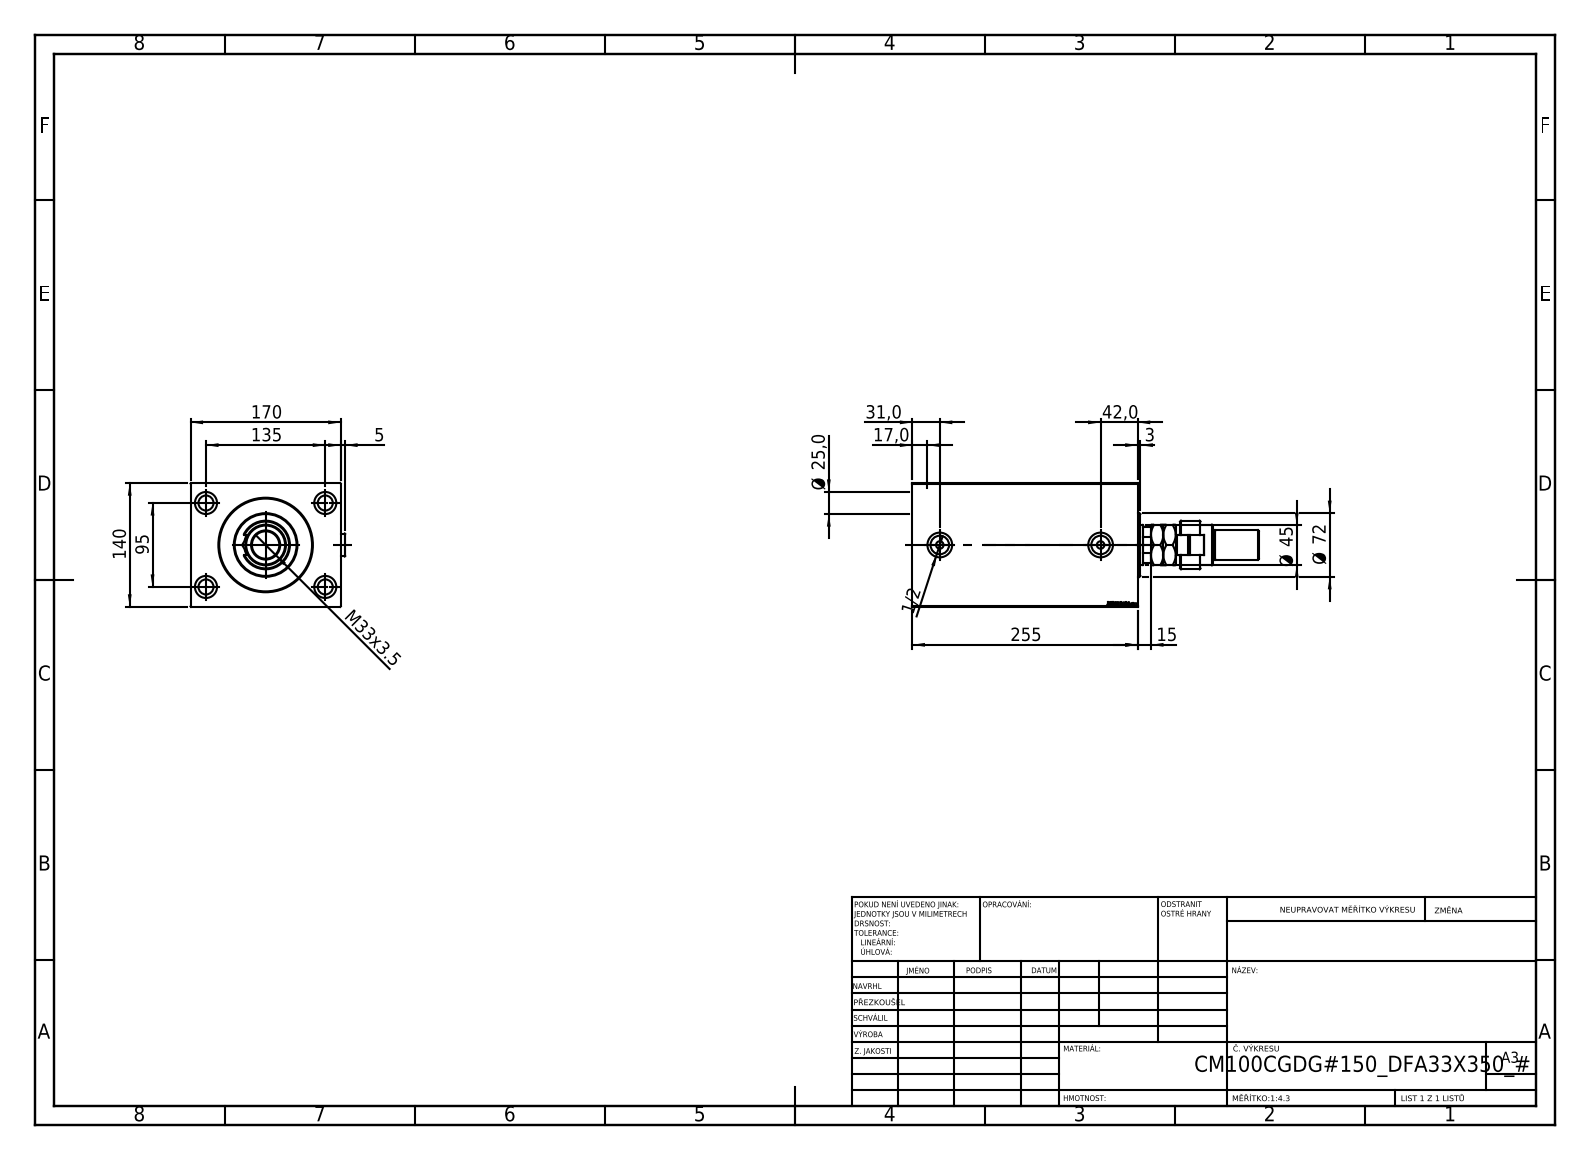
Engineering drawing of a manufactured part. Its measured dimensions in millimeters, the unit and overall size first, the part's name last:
Units: millimetres
Overall size (bounding box): 392 × 174.9 × 140
Round holes (diameter × count): ⌀17 ×4, ⌀25 ×4, ⌀8.5 ×2, ⌀20.96 ×2, ⌀28 ×2, ⌀31.5 ×1, ⌀39 ×1, ⌀45 ×1, ⌀48.5 ×1, ⌀100 ×1, ⌀102 ×1, ⌀105 ×1
Round bosses / shafts (diameter × count): ⌀26 ×2, ⌀72 ×1, ⌀55 ×1, ⌀46 ×1, ⌀35 ×1, ⌀33 ×1, ⌀31 ×1, ⌀22 ×1
Partial cylindrical surfaces — rounded edges, fillets, slot ends (radius × count): R11.5 ×1, R22 ×1
Main face-to-face distances: 140, 170, 255, 26, 229, 15, 90, 240, 64, 214
Hole centre spacings: 82.54, 95, 135, 165.08, 182
Volume: 5 003 000 mm³ · Surface area: 459 820 mm²
Bodies: 7 solids, 1004 faces (471 planar, 91 cylindrical, 442 other)
Part name (STEP PRODUCT): V450CM_VC_B; V450CM_C_VCP; MFA; V450CM_C_Body (+2 more)
STEP written by: SolidWorks 2019 (CONFIG_CONTROL_DESIGN)
